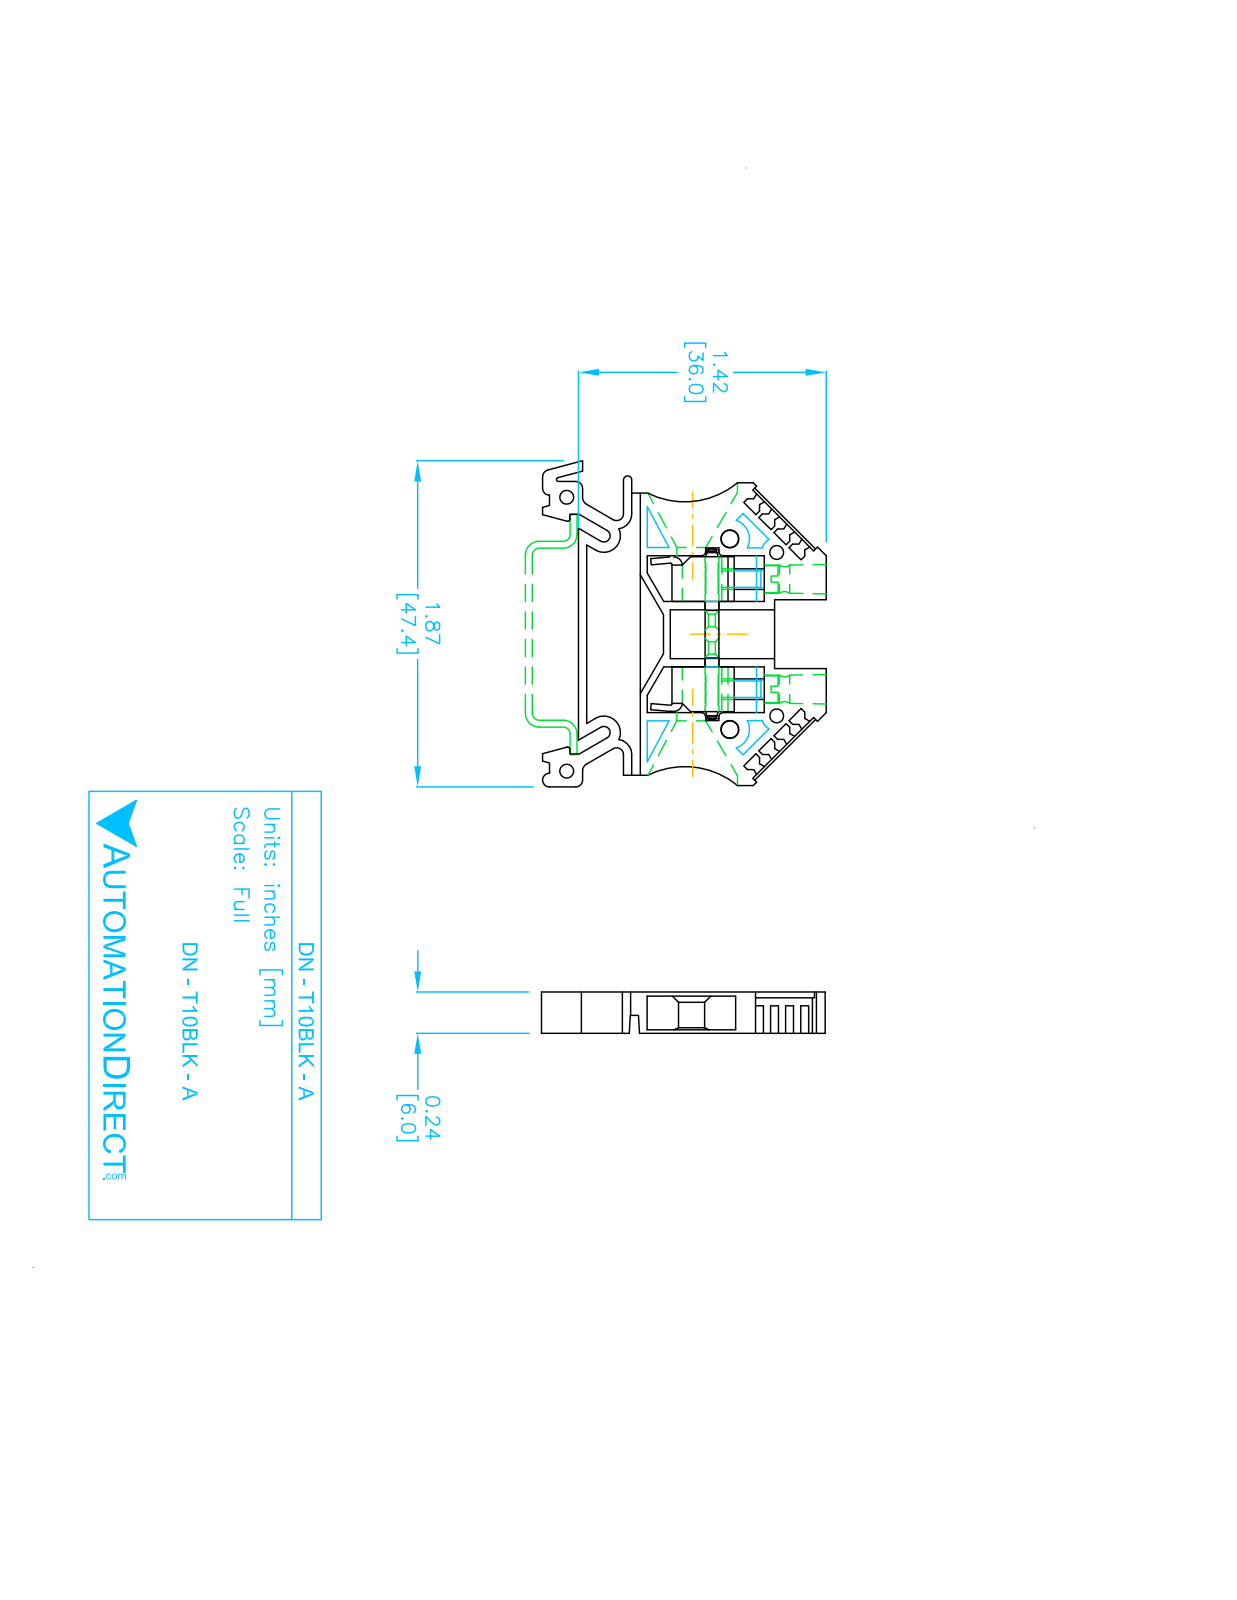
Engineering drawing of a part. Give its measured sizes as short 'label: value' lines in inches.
name: DN-T10BLK-A
written by: SolidWorks 2017 (AUTOMOTIVE_DESIGN)
unit: in
bodies: 1 solid, 181 faces (141 planar, 40 cylindrical, 0 other)
size: 1.866 × 1.622 × 0.236
volume: 0.381 in³; area: 7.683 in²
holes: 2× ⌀0.079, 2× ⌀0.172
rounds: 7× R0.039, 2× R0.012, 2× R0.035, 2× R0.047, 2× R0.087, 2× R0.094, 2× R0.472, 1× R0.011
face distances: 0.228, 0.236, 0.142, 0.094, 0.047, 0.087, 0.134, 0.354, 0.071, 0.307
hole spacings: 0.63, 1.567
